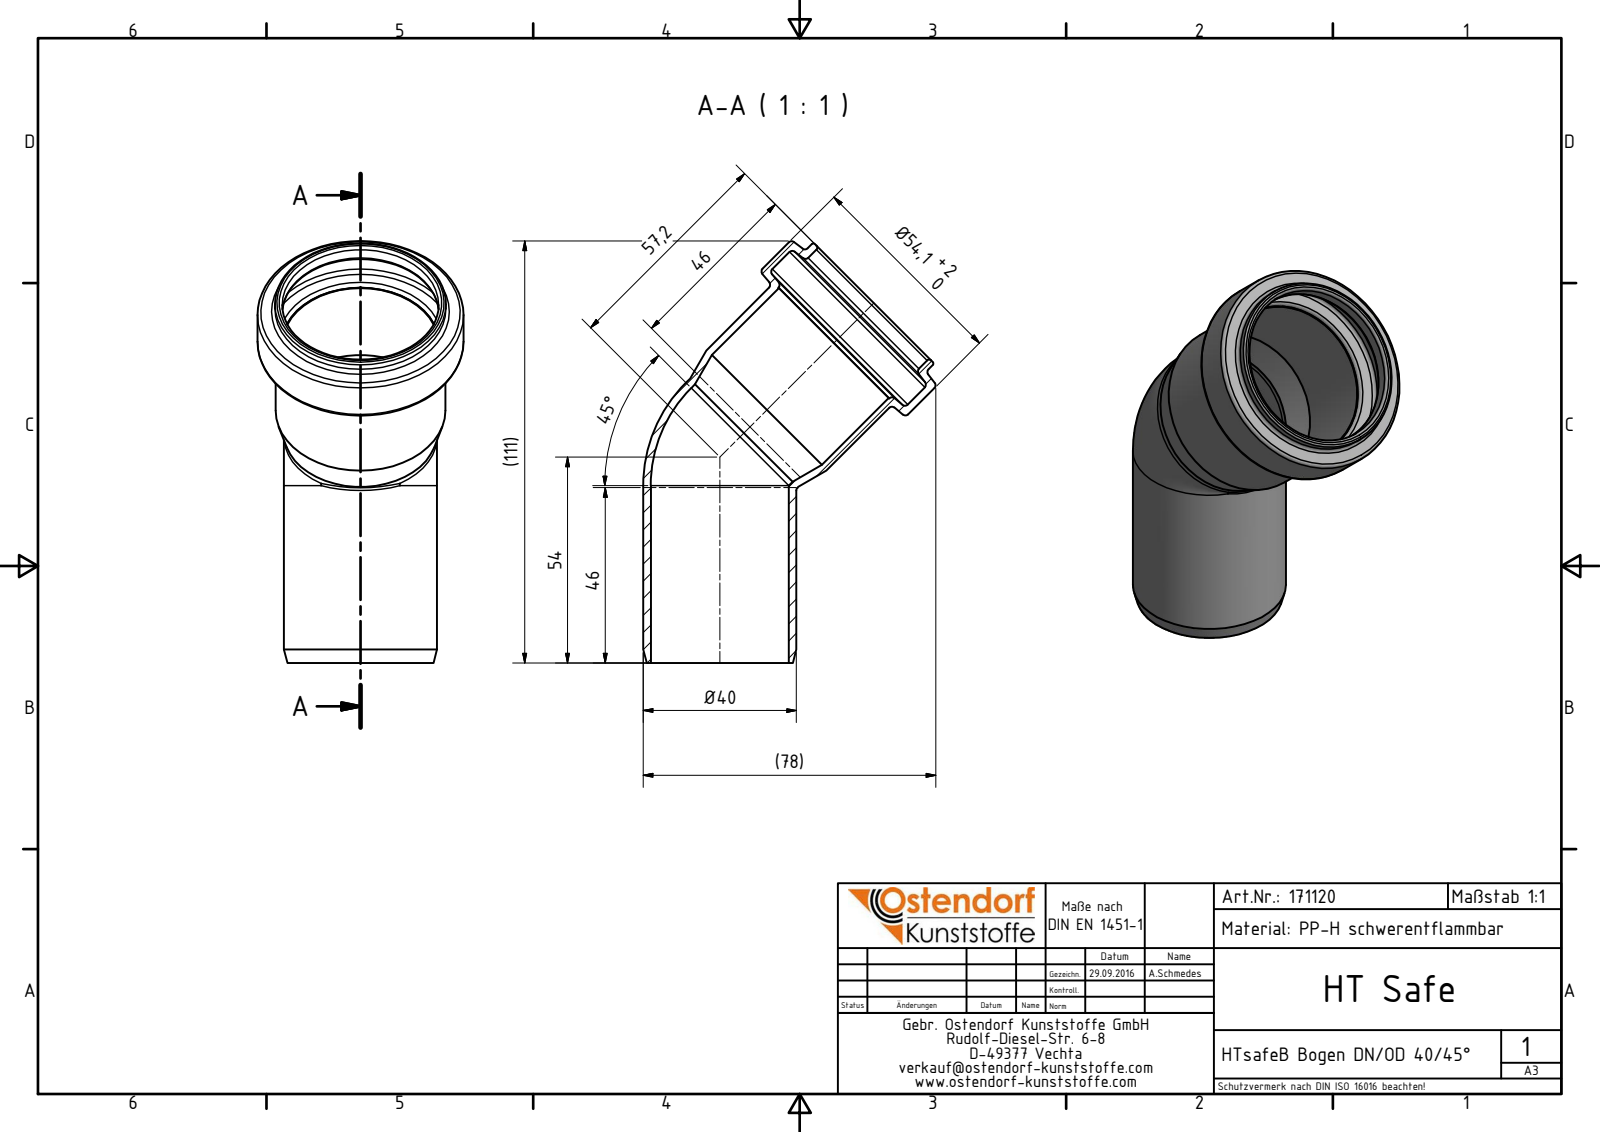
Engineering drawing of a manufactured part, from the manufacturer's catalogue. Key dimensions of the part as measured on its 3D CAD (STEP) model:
Part name (STEP PRODUCT): 171120 HTsafeB DN_OD 40_45°
STEP written by: Autodesk Inventor 2016 (AUTOMOTIVE_DESIGN)
Units: millimetres
Bodies: 1 solid, 34 faces (3 planar, 11 cylindrical, 20 other)
Overall size (bounding box): 110.69 × 76.79 × 54.1
Volume: 29 264 mm³ · Surface area: 30 887 mm²
Round holes (diameter × count): ⌀36.2 ×2, ⌀40.8 ×1, ⌀41.1 ×1, ⌀50.3 ×1
Round bosses / shafts (diameter × count): ⌀40.2 ×2, ⌀54.1 ×1, ⌀44.9 ×1, ⌀44.6 ×1
Main face-to-face distances: 14.9
